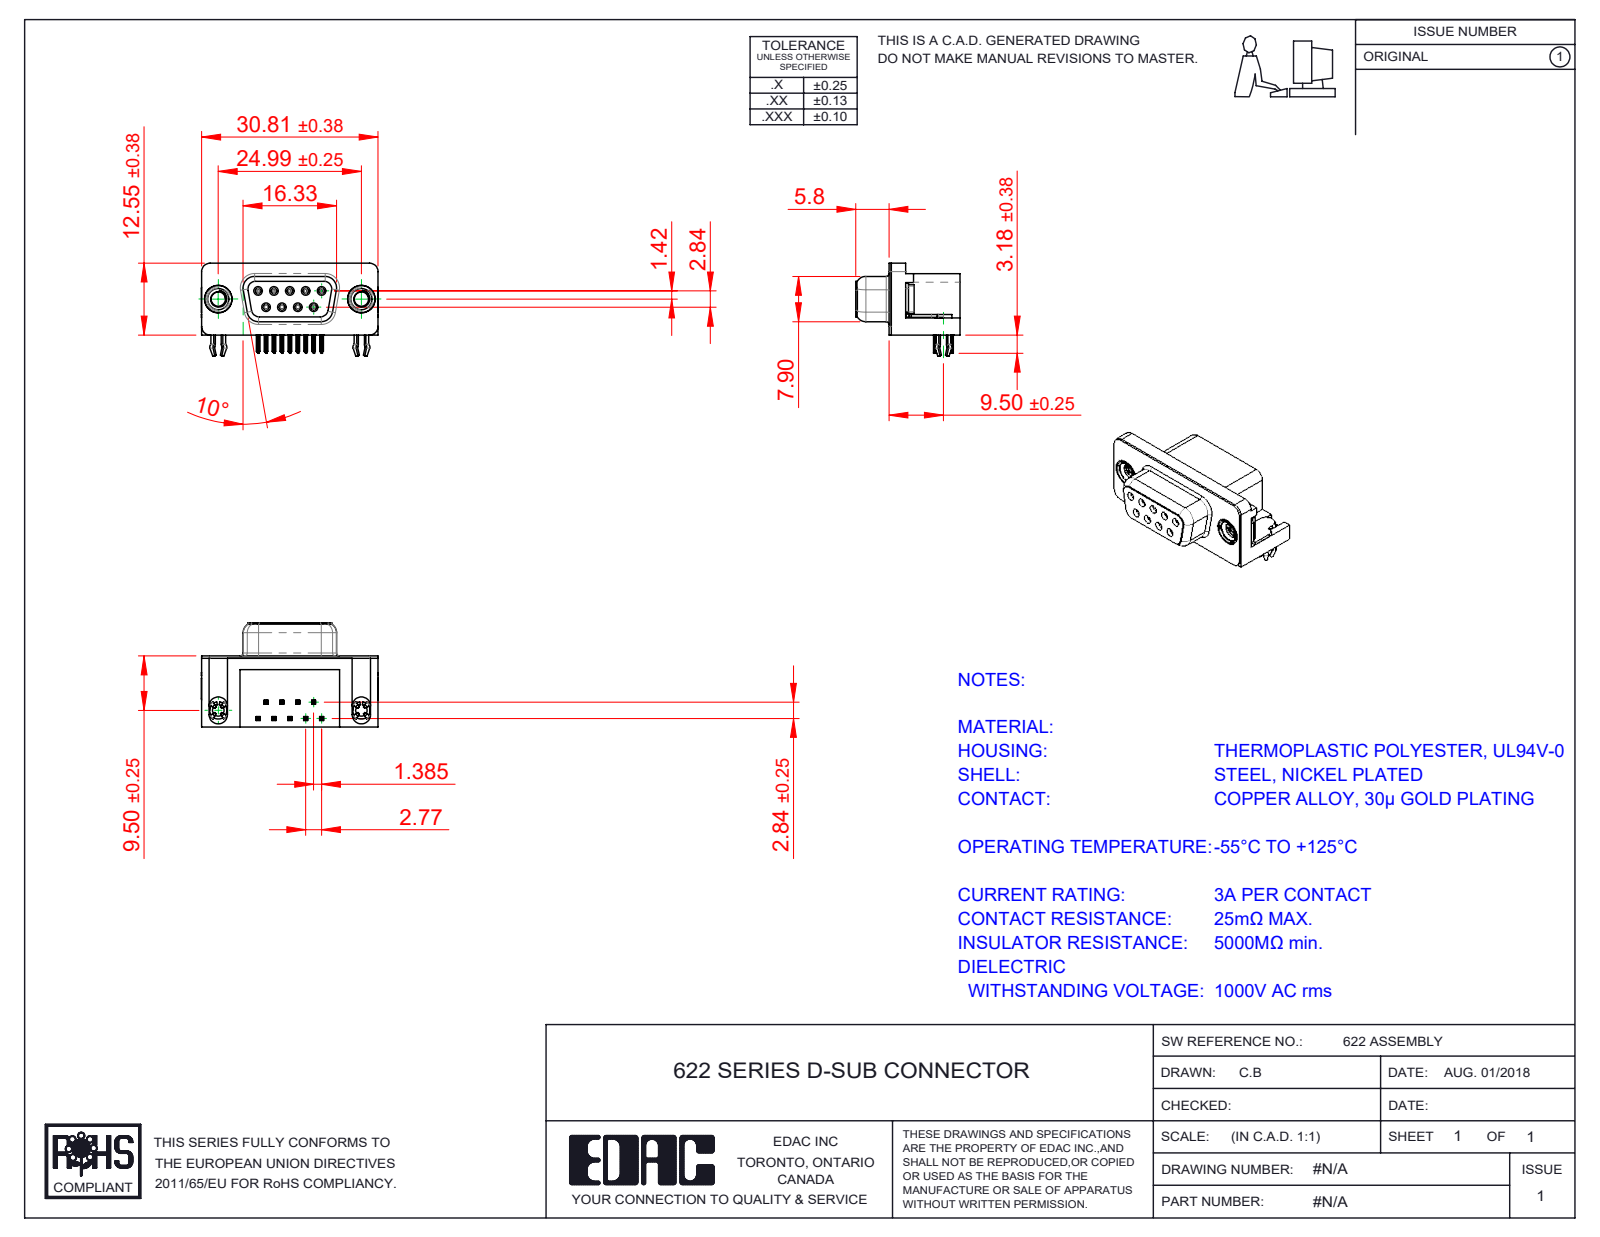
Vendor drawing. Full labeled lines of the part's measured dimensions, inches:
Part name (STEP PRODUCT): 622 4-40 Threaded Board Mount; 622-009-668-555; 622 Socket Bottom; 622 Shell_9 Socket (+3 more)
STEP written by: SolidWorks 2016 (CONFIG_CONTROL_DESIGN)
Units: inches
Bodies: 15 solids, 1602 faces (684 planar, 432 cylindrical, 486 other)
Overall size (bounding box): 1.216 × 0.717 × 0.619
Volume: 0.228 in³ · Surface area: 7.992 in²
Round holes (diameter × count): ⌀0.031 ×9, ⌀0.035 ×9, ⌀0.089 ×2, ⌀0.098 ×2, ⌀0.157 ×2, ⌀0.189 ×2, ⌀0.197 ×2
Round bosses / shafts (diameter × count): ⌀0.047 ×9, ⌀0.193 ×2, ⌀0.187 ×2, ⌀0.154 ×2, ⌀0.128 ×2
Partial cylindrical surfaces — rounded edges, fillets, slot ends (radius × count): R0.004 ×72, R0.006 ×36, R0.014 ×18, R0.039 ×18, R0.013 ×9, R0.01 ×8, R0.053 ×8, R0.063 ×8
Main face-to-face distances: 0.016, 0.472, 0.488, 0.014, 0.114, 0.098, 0.244, 0.407, 0.374, 0.228
Hole centre spacings: 0.124, 0.109, 0.218, 0.198, 0.198, 0.327, 0.294, 0.295
